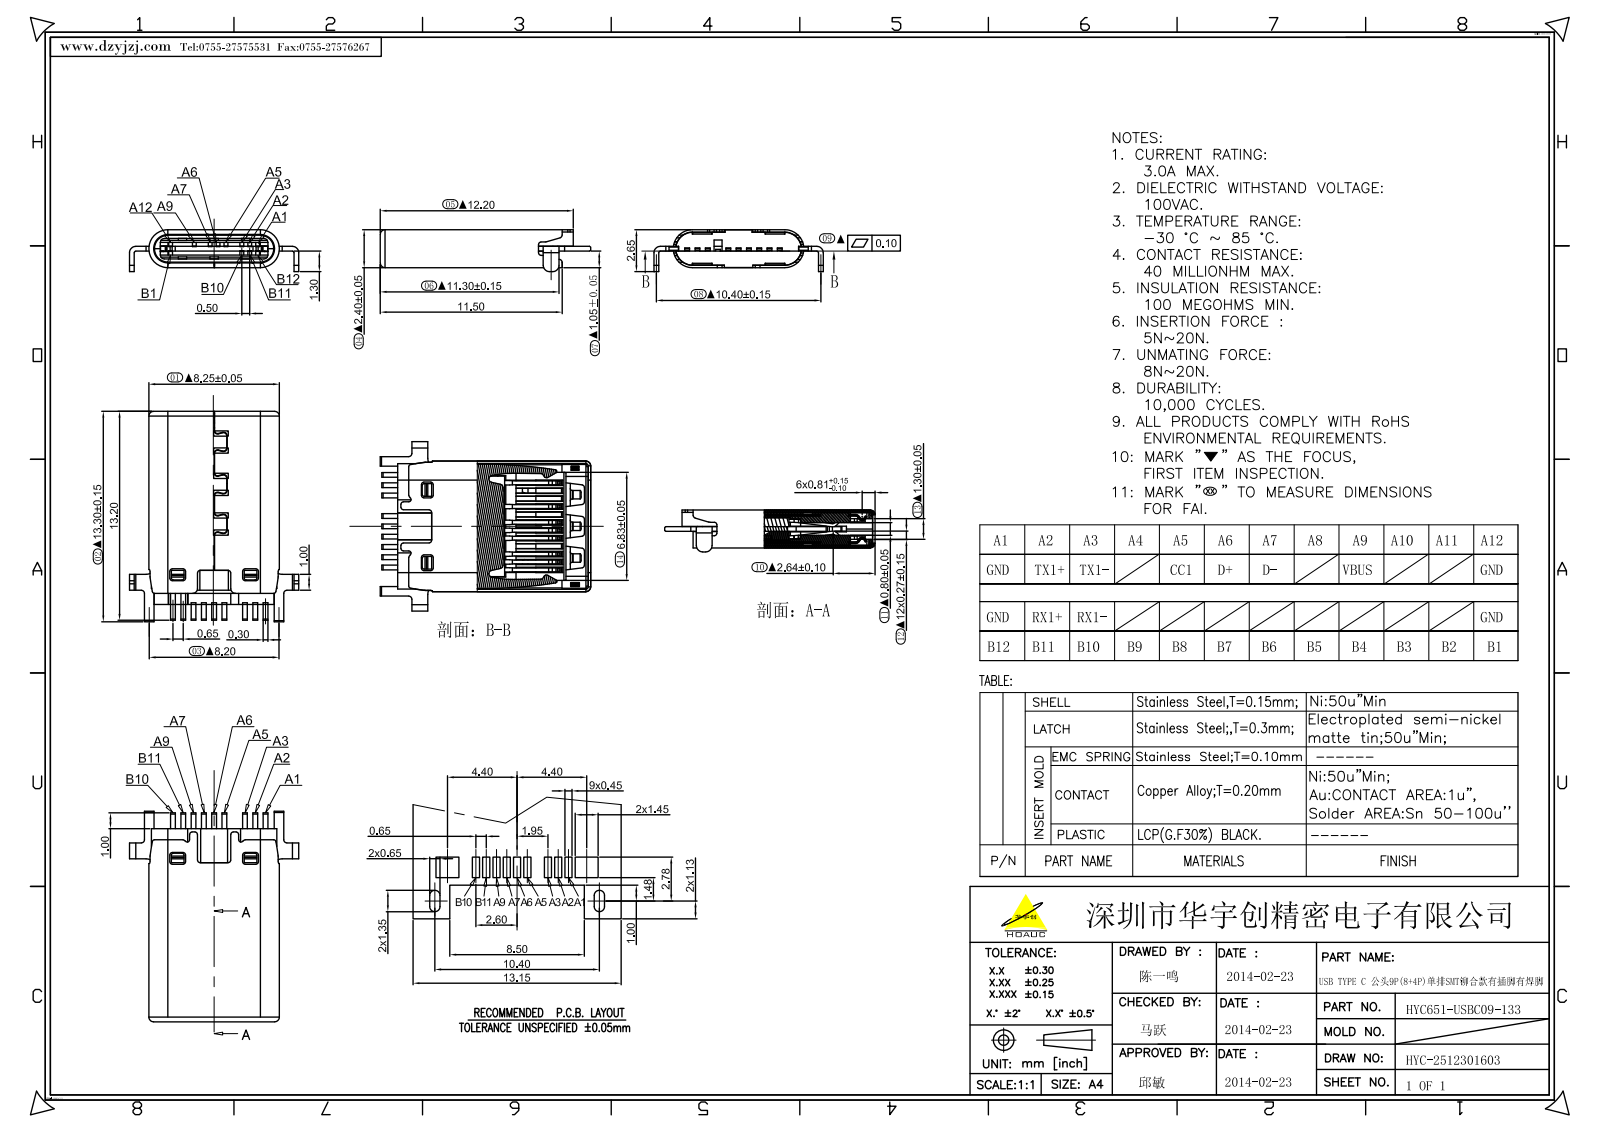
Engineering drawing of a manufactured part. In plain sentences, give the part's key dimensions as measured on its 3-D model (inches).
The part is named "XDS-A_TC_2_M_215B". Its 3-D file was written by "CREO PARAMETRIC BY PTC INC, 2022073 (CONFIG_CONTROL_DESIGN)". It is 1 solid with 565 faces: 396 planar, 165 cylindrical and 4 other. Overall it measures 0.524 by 0.421 by 0.104 inches. Its volume is 0.011 cubic inches and its surface area 0.694 square inches. Partial cylindrical surfaces (rounded edges, fillets, slot ends): 32 of radius 0.006, 13 of radius 0.008, 10 of radius 0.004, 10 of radius 0.012, 6 of radius 0.007, 6 of radius 0.009, 6 of radius 0.01, 6 of radius 0.041. The main face-to-face distances are 0.031, 0.094, 0.041, 0.063, 0.022, 0.02, 0.053, 0.035, 0.073, 0.051.
